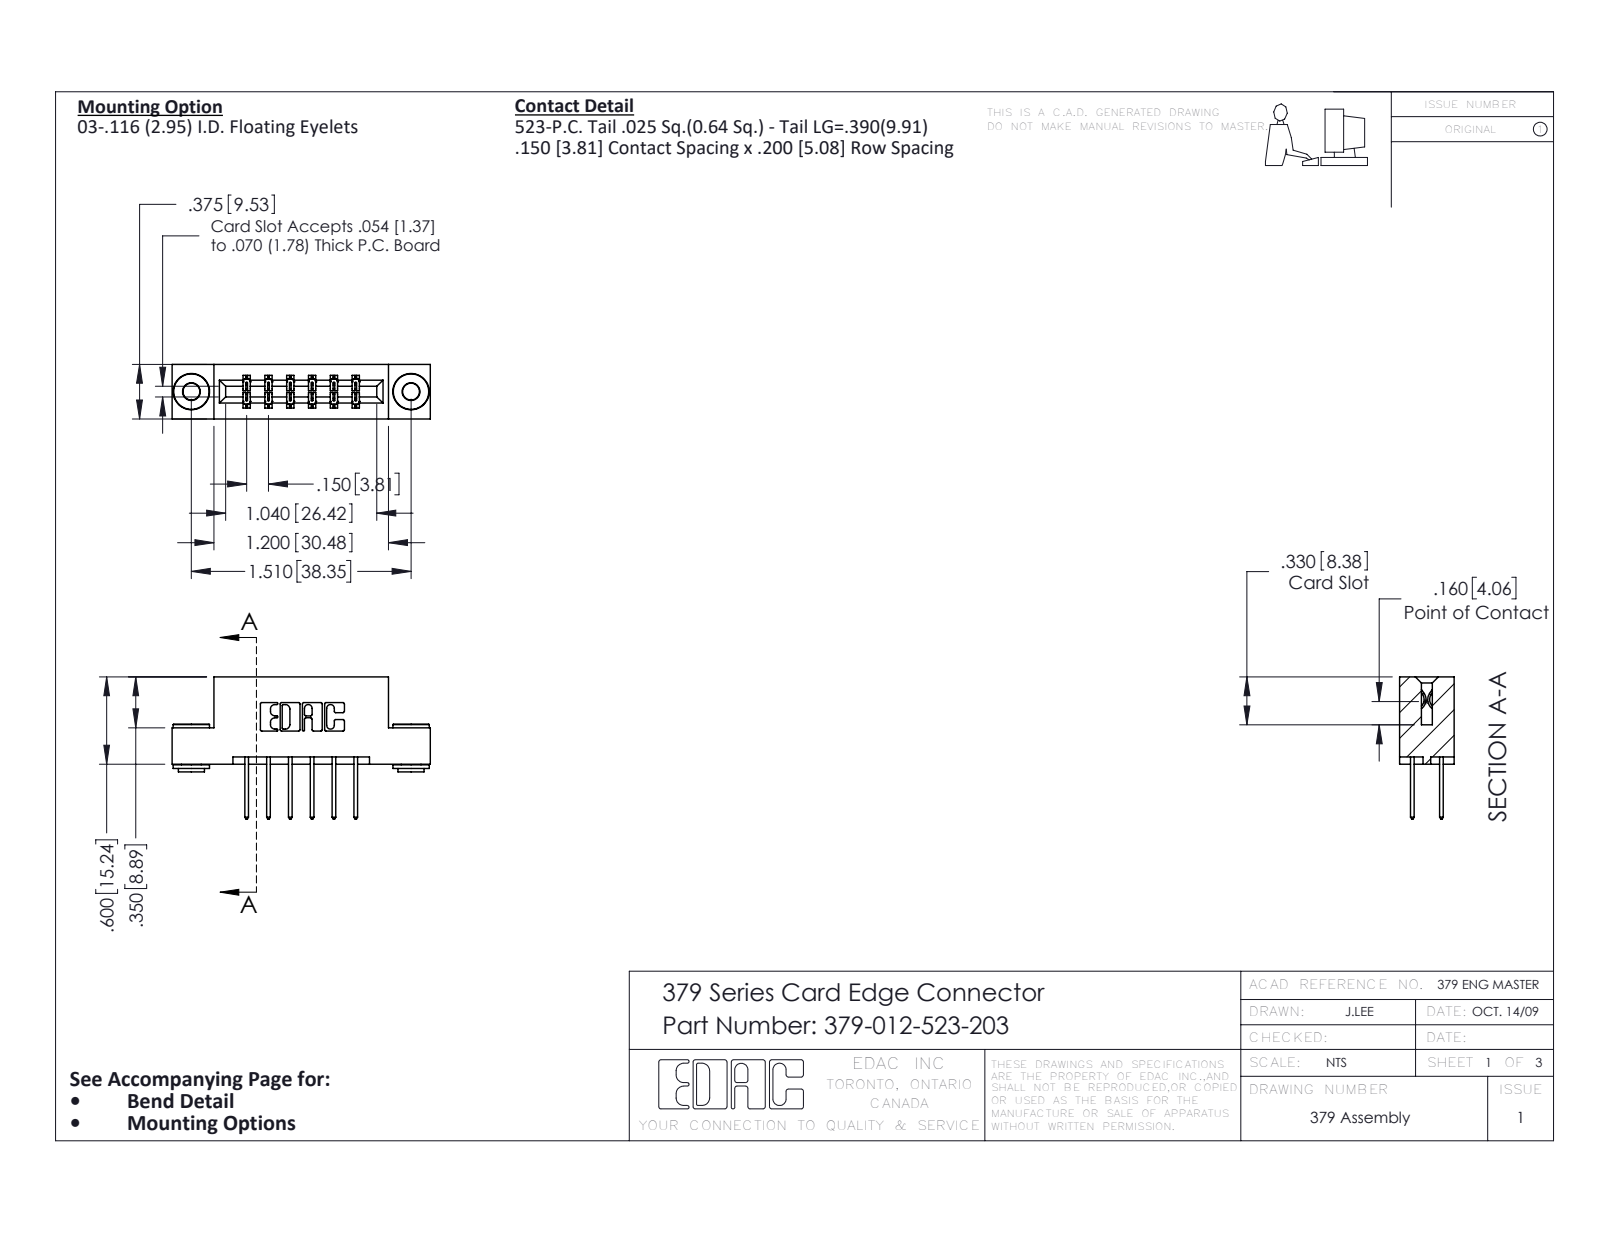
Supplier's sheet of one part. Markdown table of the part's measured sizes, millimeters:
| quantity | value |
| --- | --- |
| part name | 379-012-523-203; 379 Part_Flush - .156 Dia - TH; 345-250-002_345-250-002-102; 345-292-001_345-293-123 |
| STEP written by | SolidWorks 2016 (CONFIG_CONTROL_DESIGN) |
| units | millimeters |
| bodies | 15 solids, 776 faces (512 planar, 256 cylindrical, 8 other) |
| overall size | 45.1 × 24.8 × 9.5 |
| volume | 4 390 mm³ |
| surface area | 4 943 mm² |
| round holes (diameter × count) | 2.9 × 2, 4 × 2 |
| round bosses / shafts (diameter × count) | 6.4 × 2, 4.6 × 2, 3.5 × 2 |
| partial cylindrical surfaces (radius × count) | 0.3 × 22, 0.2 × 18, 0.3 × 12, 0.2 × 6, 0.8 × 6, 0.7 × 3, 0.4 × 2, 0.6 × 2 |
| main face-to-face distances | 7.6, 5.1, 3.8, 9.5, 1.3, 2.5, 6.4, 8.9, 1.9, 14 |
| hole center spacings | 38.4 |
